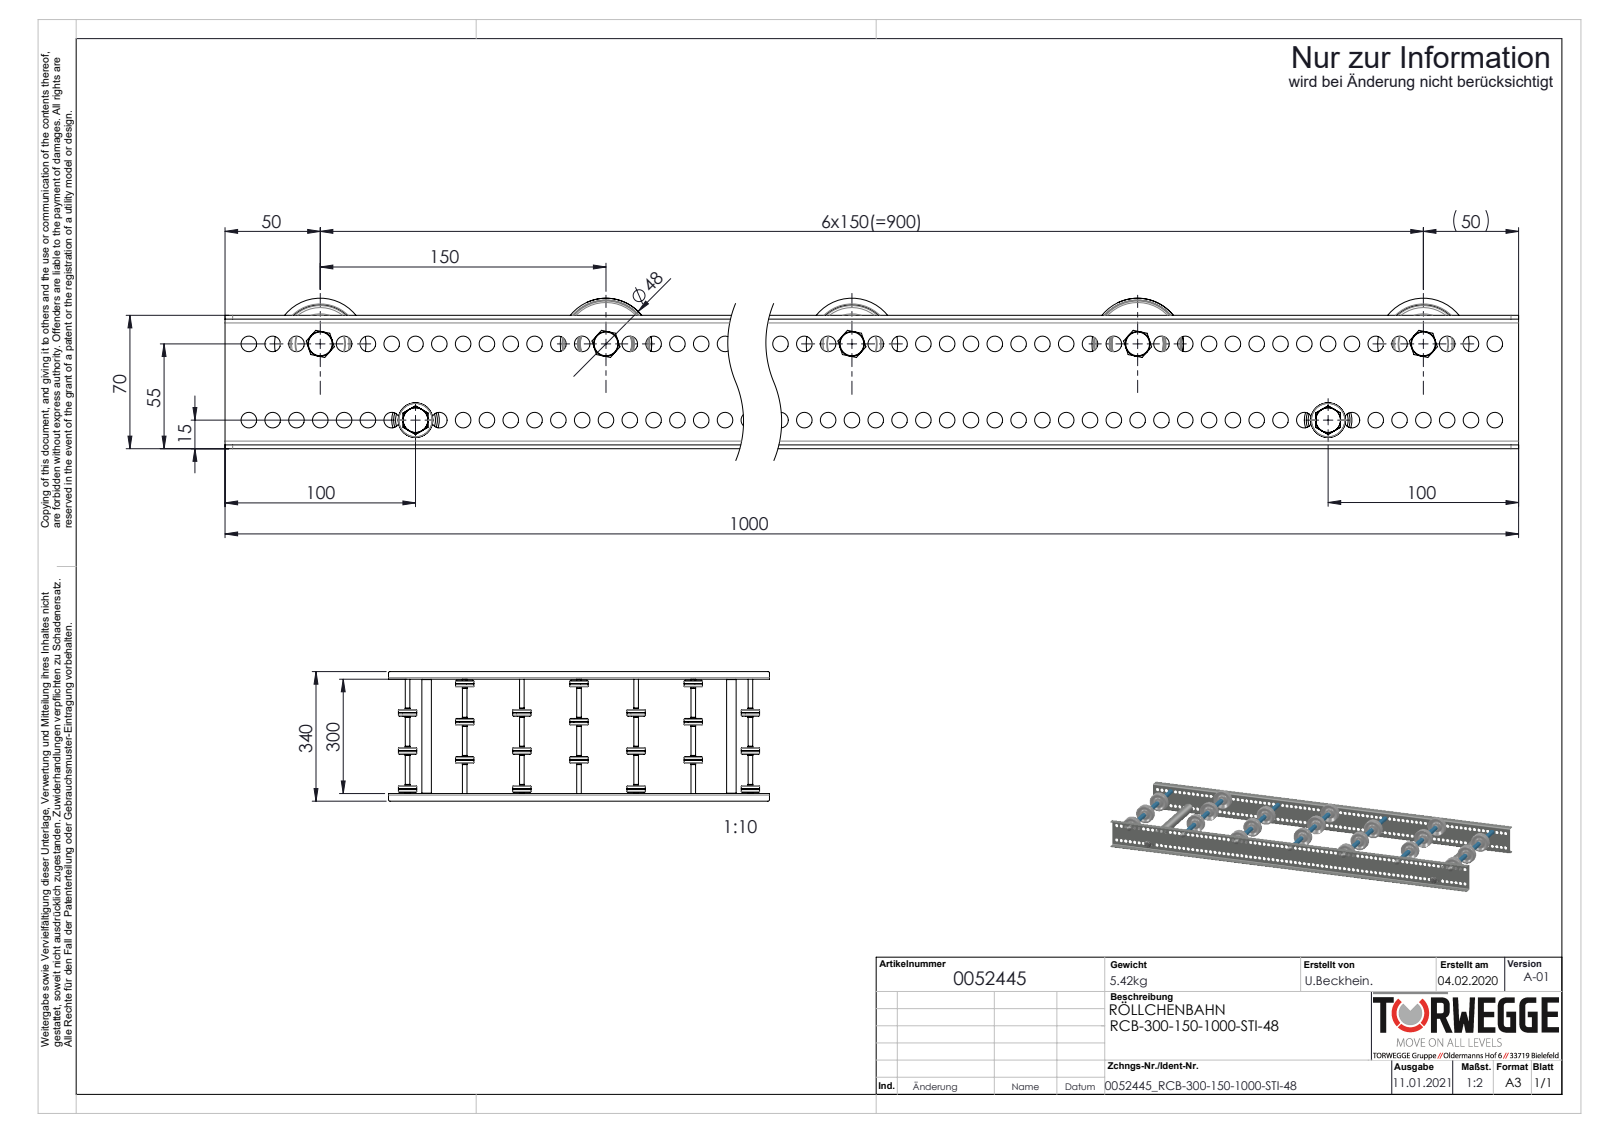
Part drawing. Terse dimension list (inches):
name: K0011528_2200-48-8; 0046278_KB-ROHR-12X1,75mm_KFG_L76; Röllchenachse-für-Konfiguration_EL300 Stahl; Hutmutter_DIN_1587_M8 (+5 more)
written by: SolidWorks 2020 (AUTOMOTIVE_DESIGN)
unit: in
bodies: 96 solids, 3166 faces (624 planar, 1388 cylindrical, 1154 other)
size: 39.37 × 13.386 × 3.11
volume: 68.71 in³; area: 1 459 in²
holes: 158× ⌀0.323, 7× ⌀0.262, 7× ⌀0.315, 7× ⌀0.38, 7× ⌀0.591, 7× ⌀1.614, 2× ⌀0.268, 2× ⌀0.827
bosses: 7× ⌀1.89, 7× ⌀0.512, 7× ⌀0.492, 7× ⌀0.488, 7× ⌀0.472, 7× ⌀0.453, 2× ⌀0.984, 2× ⌀0.315
rounds: 8× R0.157, 4× R0.079
face distances: 0.079, 11.89, 2.677, 11.969, 11.811, 3.937, 2.598, 2.756, 2.992, 0.472
hole spacings: 0.492, 0.984, 1.476, 1.969, 2.461, 2.953, 3.445, 3.937
